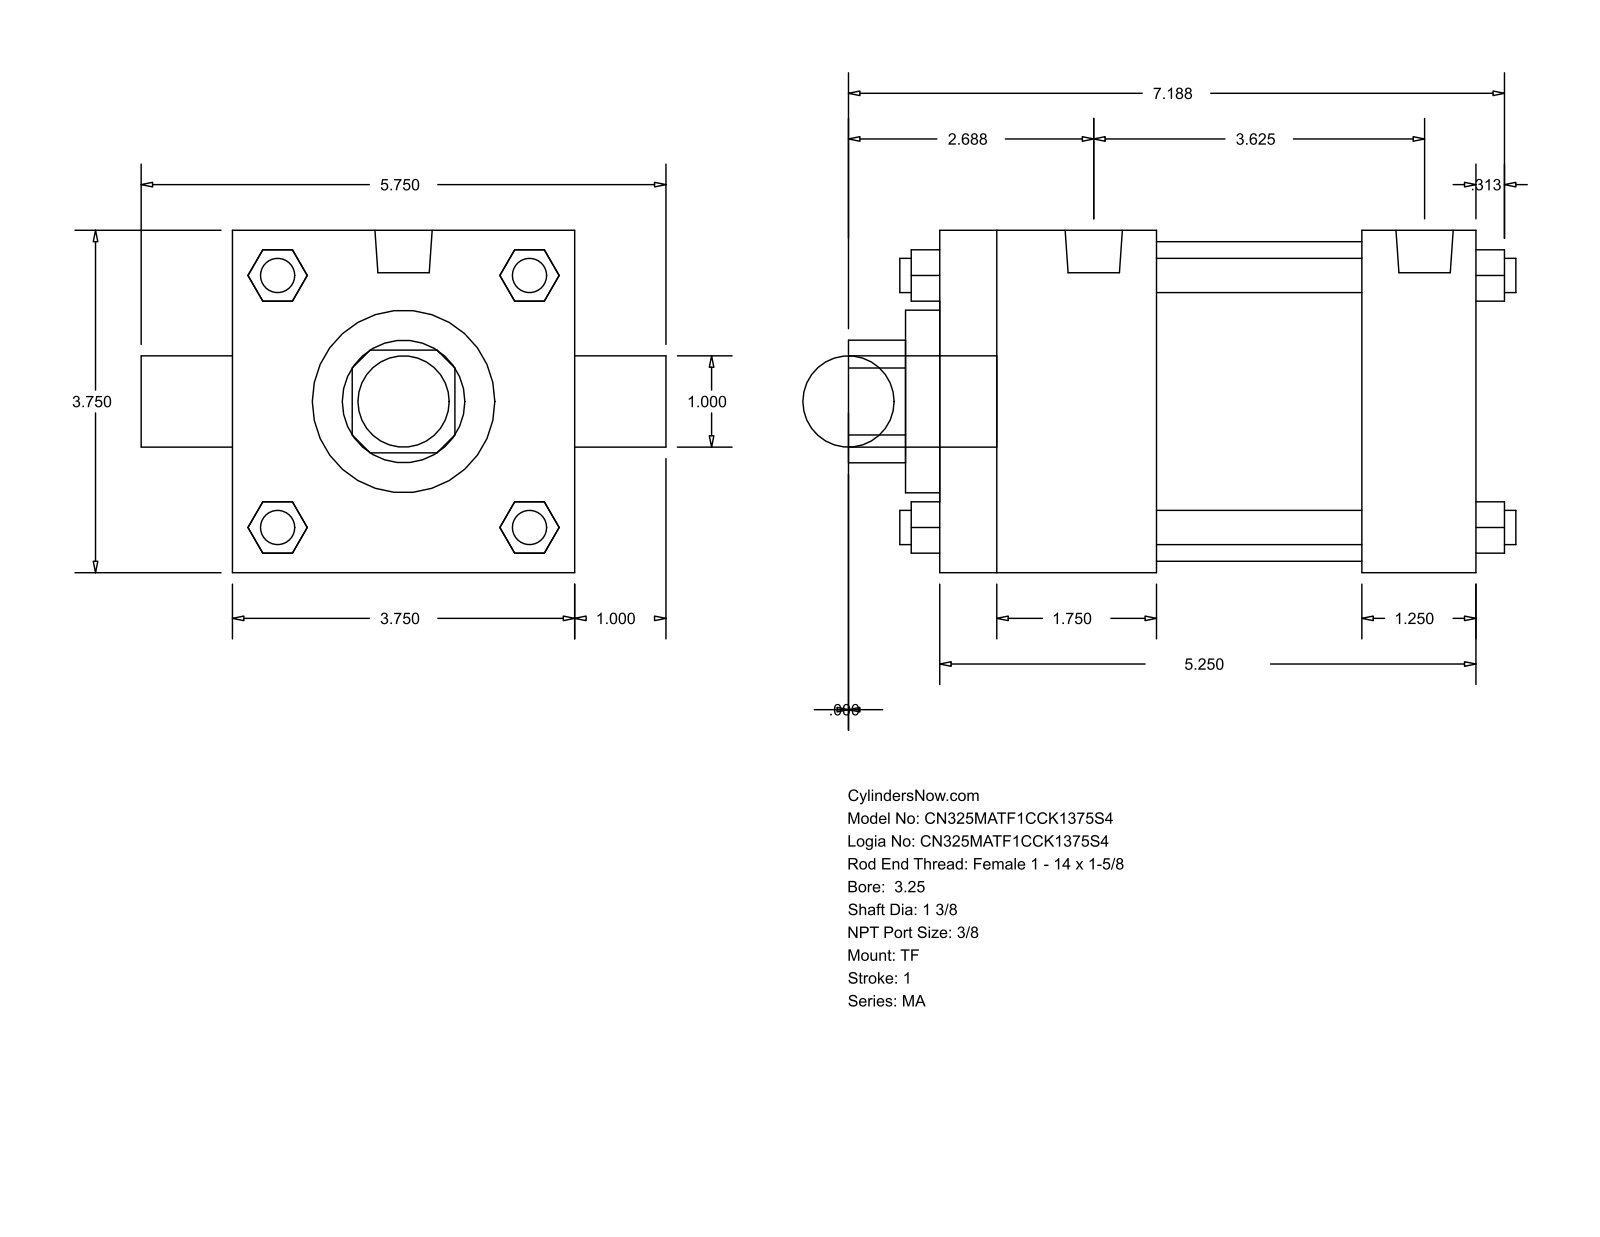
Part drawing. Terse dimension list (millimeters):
name: MA_TF__0325_1.375
written by: GSSL Pune (CONFIG_CONTROL_DESIGN)
unit: mm
bodies: 0 solids, 120 faces (92 planar, 28 cylindrical, 0 other)
size: 185.74 × 146.05 × 95.25
holes: 1× ⌀25.4, 1× ⌀34.92, 1× ⌀50.8, 1× ⌀88.9
bosses: 4× ⌀9.53, 3× ⌀11.11, 2× ⌀15.93, 1× ⌀25.4
rounds: 1× R17.06
face distances: 95.24, 149.22, 60.32, 117.48, 57.16, 88.9, 31.74, 9.52, 69.84, 127
